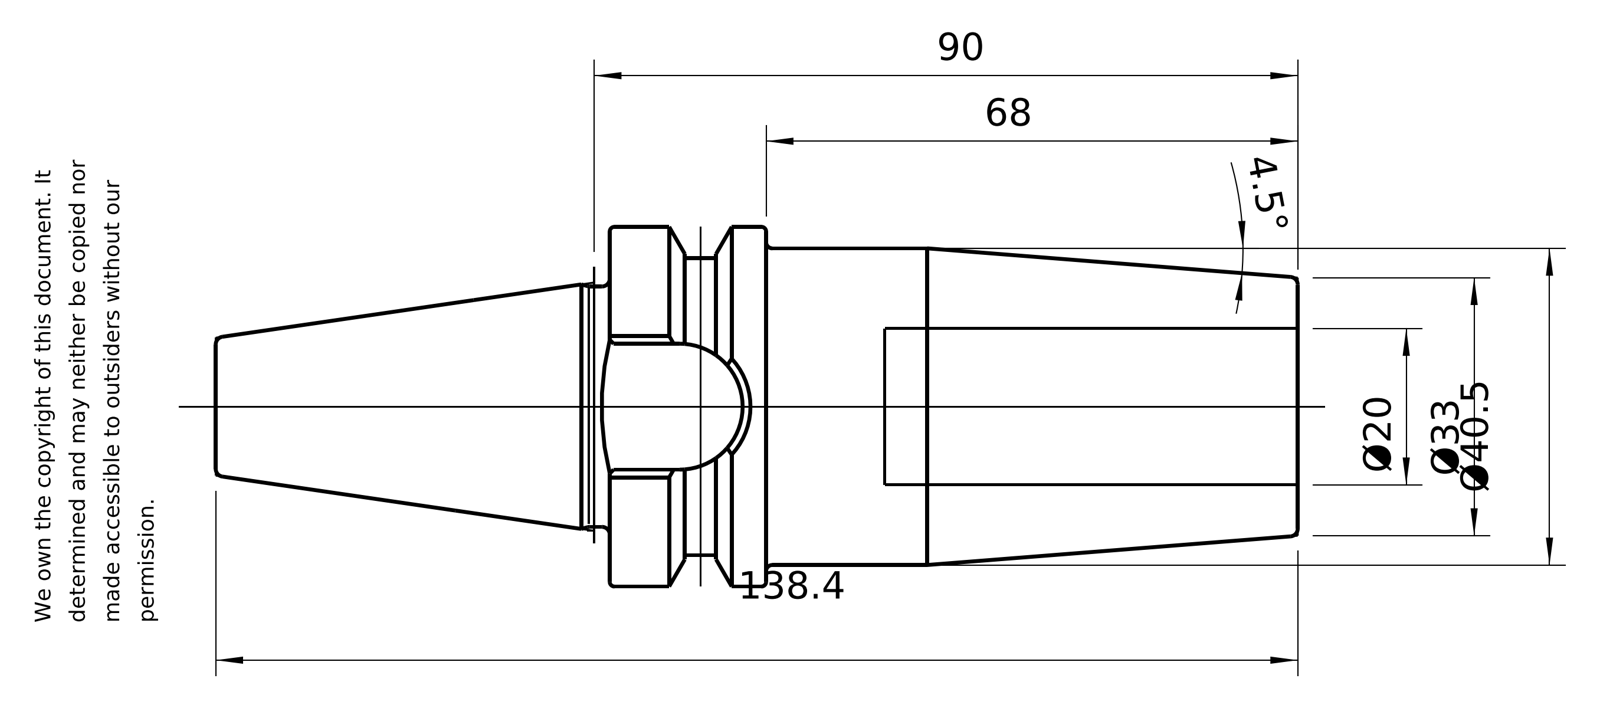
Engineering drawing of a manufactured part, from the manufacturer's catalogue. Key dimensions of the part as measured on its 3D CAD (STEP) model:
Part name (STEP PRODUCT): 30-640-20
STEP written by: PRO/ENGINEER BY PARAMETRIC TECHNOLOGY CORPORATION, 2010430 (CONFIG_CONTROL_DESIGN)
Units: millimetres
Bodies: 1 solid, 96 faces (26 planar, 22 cylindrical, 48 other)
Overall size (bounding box): 138.4 × 45.98 × 45.98
Volume: 110 130 mm³ · Surface area: 22 694 mm²
Round holes (diameter × count): ⌀10.11 ×1, ⌀12.51 ×1, ⌀13 ×1, ⌀20 ×1
Round bosses / shafts (diameter × count): ⌀45.98 ×1, ⌀40.5 ×1, ⌀30.75 ×1, ⌀12.01 ×1
Partial cylindrical surfaces — rounded edges, fillets, slot ends (radius × count): R8.1 ×1, R18.88 ×1
Main face-to-face distances: 88, 36, 52, 32.3, 20, 16, 68, 16.2, 50.4, 70.4
